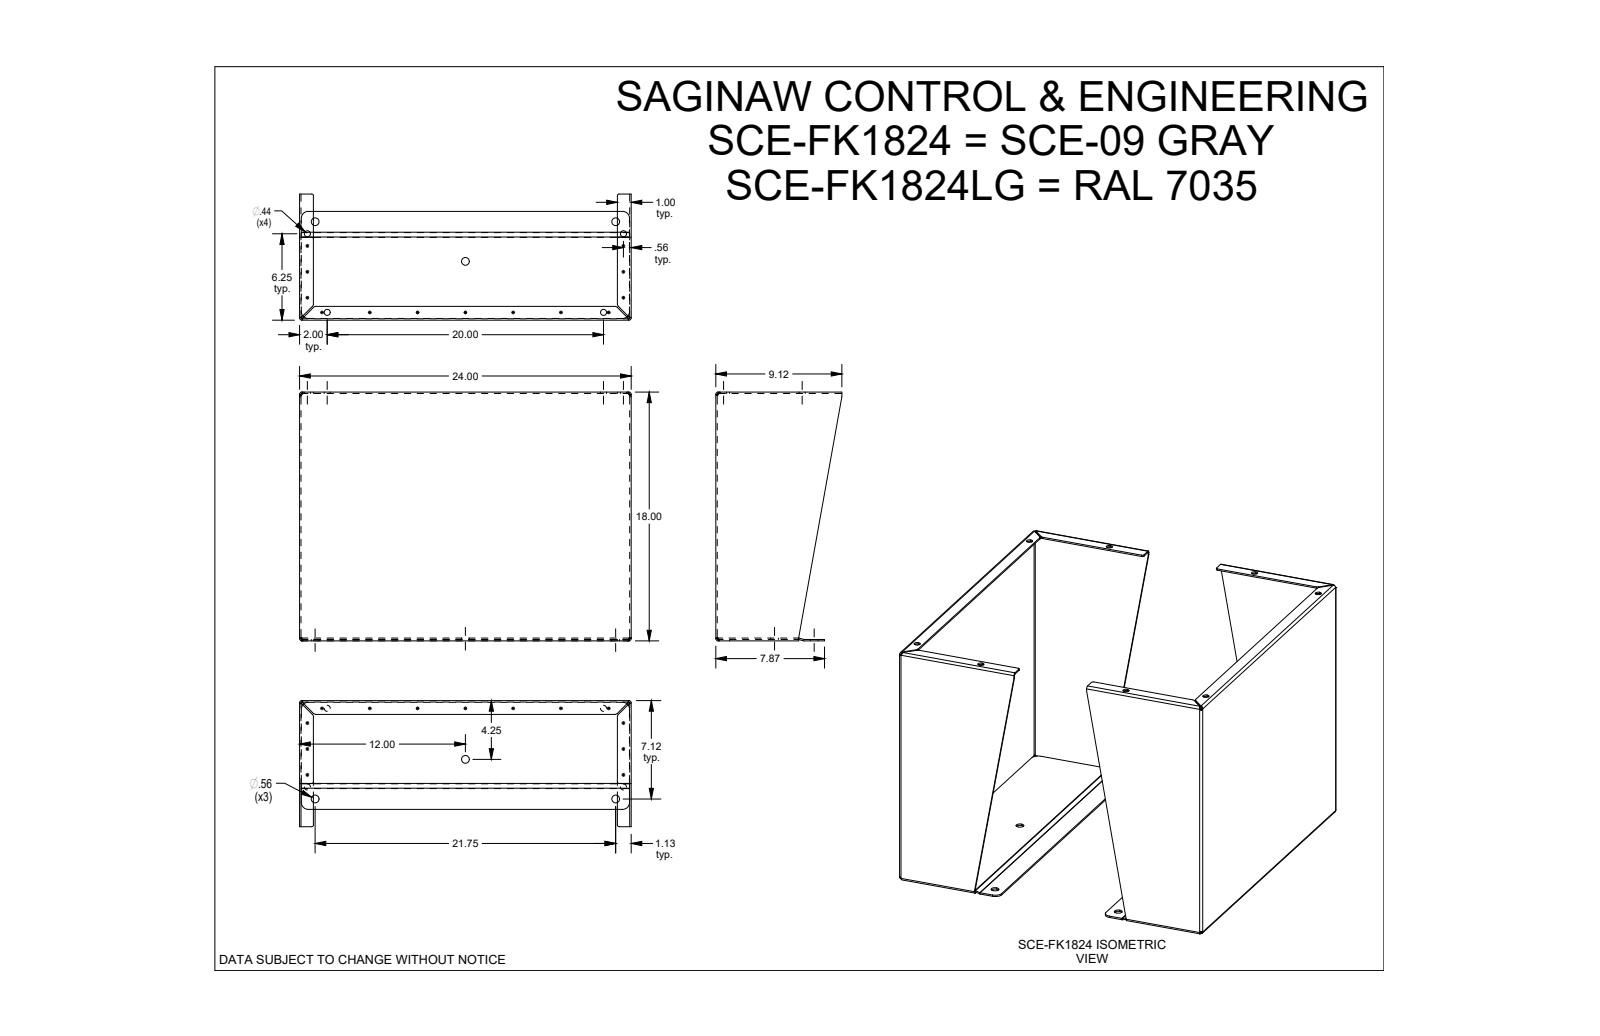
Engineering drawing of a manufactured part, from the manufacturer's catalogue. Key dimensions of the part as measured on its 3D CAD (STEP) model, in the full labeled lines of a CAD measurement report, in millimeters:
Part name (STEP PRODUCT): SCE-FK1824LG
STEP written by: SolidWorks 2019 (CONFIG_CONTROL_DESIGN)
Units: millimetres
Bodies: 4 solids, 214 faces (96 planar, 86 cylindrical, 32 other)
Overall size (bounding box): 609.6 × 609.6 × 457.2
Volume: 3 215 000 mm³ · Surface area: 2 460 000 mm²
Round holes (diameter × count): ⌀11.1 ×8, ⌀14.3 ×6
Partial cylindrical surfaces — rounded edges, fillets, slot ends (radius × count): R4.2 ×16, R1.6 ×12, R3.2 ×8, R5.6 ×8, R12.7 ×8, R1.6 ×6
Main face-to-face distances: 2.6, 607, 604.3, 609.6, 2.6, 454.5, 451.9, 454.6, 5.2, 457.1
Hole centre spacings: 26.3, 149, 168, 270.4, 270.7, 294.9, 415.1, 438.1
